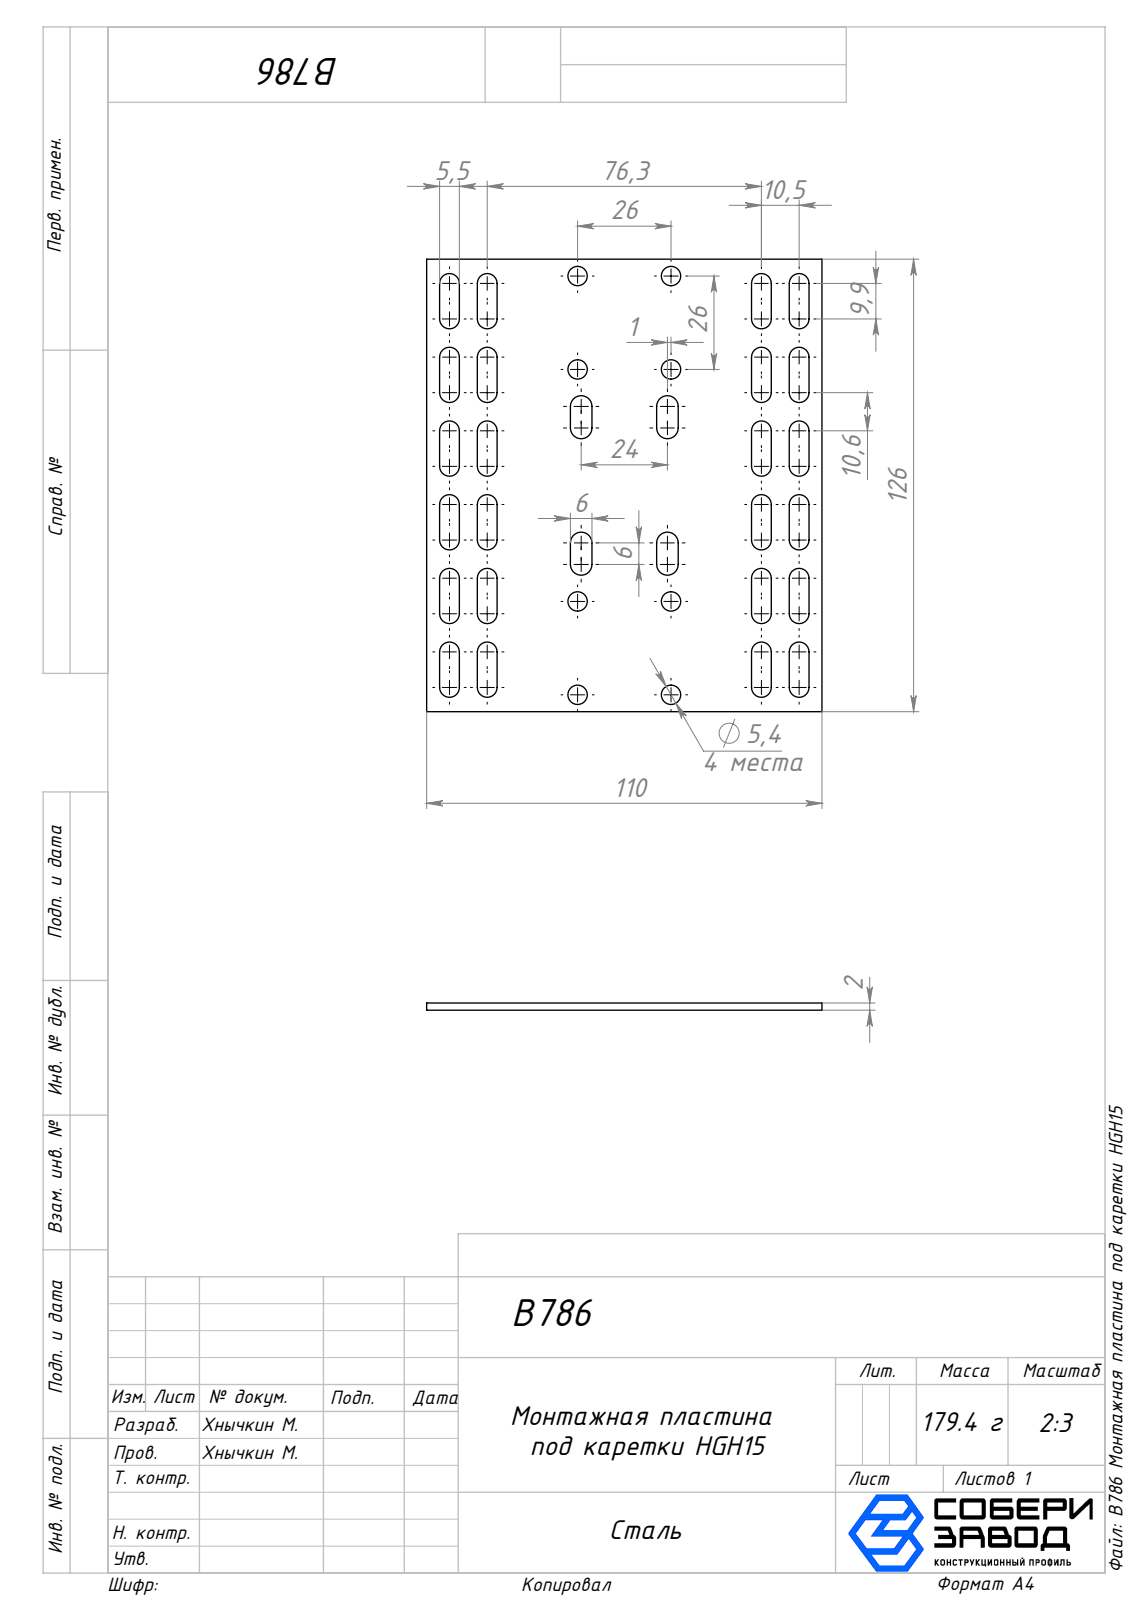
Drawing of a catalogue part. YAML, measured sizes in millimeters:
part_name: "B786 Монтажная пластина под каретки HGH15"
step_written_by: "SolidWorks 2025 (AUTOMOTIVE_DESIGN)"
units: millimeters
bodies: {solids: 1, faces: 162, planar: 62, cylindrical: 100, other: 0}
overall_size: [126, 110, 2]
volume: 23085
surface_area: 26327
round_holes:
  - {diameter: 5.4, count: 8}
partial_cylinders:
  - {radius: 2.75, count: 48}
  - {radius: 3, count: 8}
face_to_face_distances: [2, 86.8, 5.5, 10.5, 110, 9.1, 14.1, 95.9, 100.9, 5]
hole_center_spacings: [26, 36.77, 90.6, 94.26, 64.6, 69.64, 116.6, 119.46]
